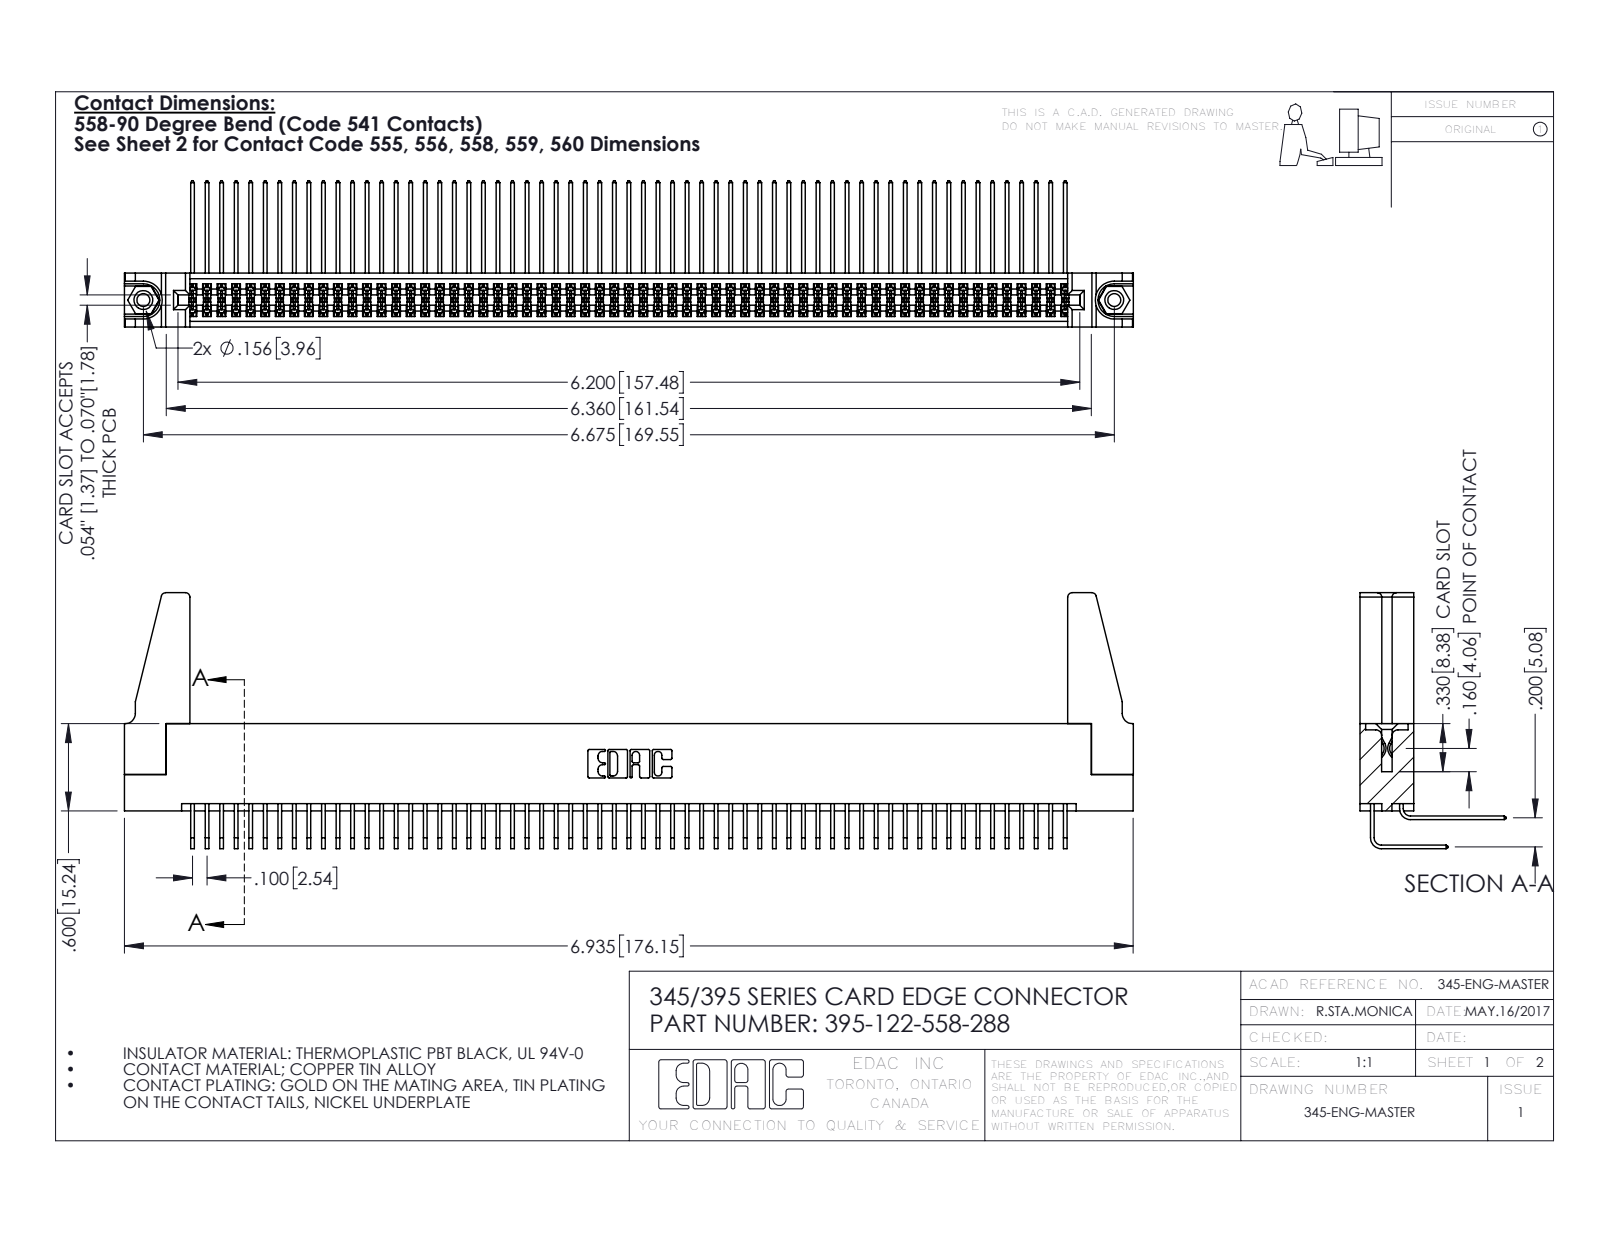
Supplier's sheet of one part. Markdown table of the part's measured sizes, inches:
| quantity | value |
| --- | --- |
| part name | 345-250-001_345-250-001-102; 345 Part_Flush Mounting Lugs - 0.156 Dia-TH; 395-122-558-288; 345-220-078_345-220-088 (+2 more) |
| STEP written by | SolidWorks 2016 (CONFIG_CONTROL_DESIGN) |
| units | inches |
| bodies | 127 solids, 6594 faces (4422 planar, 2156 cylindrical, 16 other) |
| overall size | 6.936 × 1.759 × 1.005 |
| volume | 1.297 in³ |
| surface area | 51.77 in² |
| round holes (diameter × count) | 0.089 × 2, 0.125 × 2, 0.156 × 2, 0.064 × 1 |
| round bosses / shafts (diameter × count) | 0.155 × 2 |
| partial cylindrical surfaces (radius × count) | 0.006 × 184, 0.01 × 22, 0.03 × 8, 0.007 × 6, 0.031 × 6, 0.026 × 3, 0.014 × 2, 0.019 × 2 |
| main face-to-face distances | 0.072, 0.298, 0.2, 0.37, 0.098, 0.272, 0.025, 0.225, 0.025, 0.285 |
| hole center spacings | 0.27, 6.439, 6.675 |
